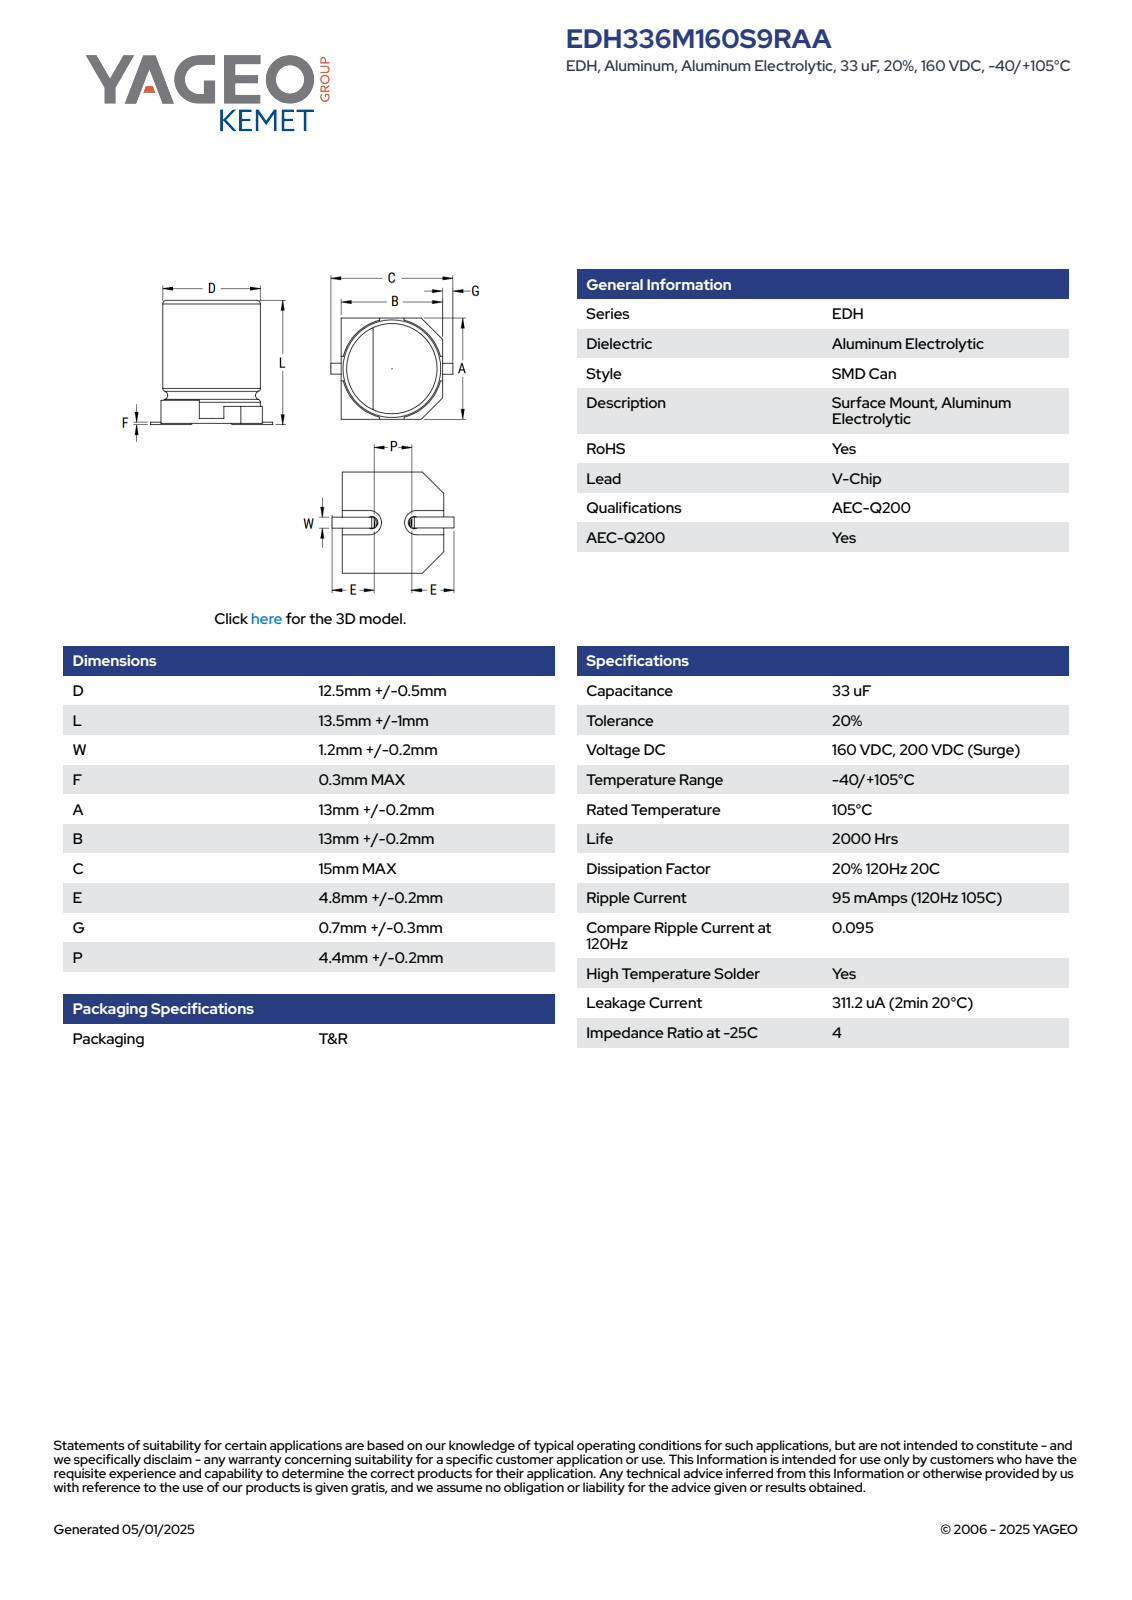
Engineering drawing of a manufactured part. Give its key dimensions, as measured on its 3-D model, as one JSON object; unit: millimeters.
{"part_name": "CAC_S_12.5X13.5_D13L14W1.45F0.3A13B13C15.2E5.1P4.8", "step_written_by": "SolidWorks 2021 (AUTOMOTIVE_DESIGN)", "units": "millimeters", "bodies": {"solids": 5, "faces": 78, "planar": 61, "cylindrical": 11, "other": 6}, "overall_size": [14.6, 14.51, 13.2], "volume_mm3": 1809, "surface_area_mm2": 1324, "round_bosses_or_shafts": [[12.43, 1]], "partial_cylinders_radius": [[0.2, 2], [5.16, 1], [6.5, 1]], "face_to_face_distances": [0.72, 14.2, 13.48, 13.2, 3.62, 2.9, 10.58, 1.02, 3.92, 14.5]}
